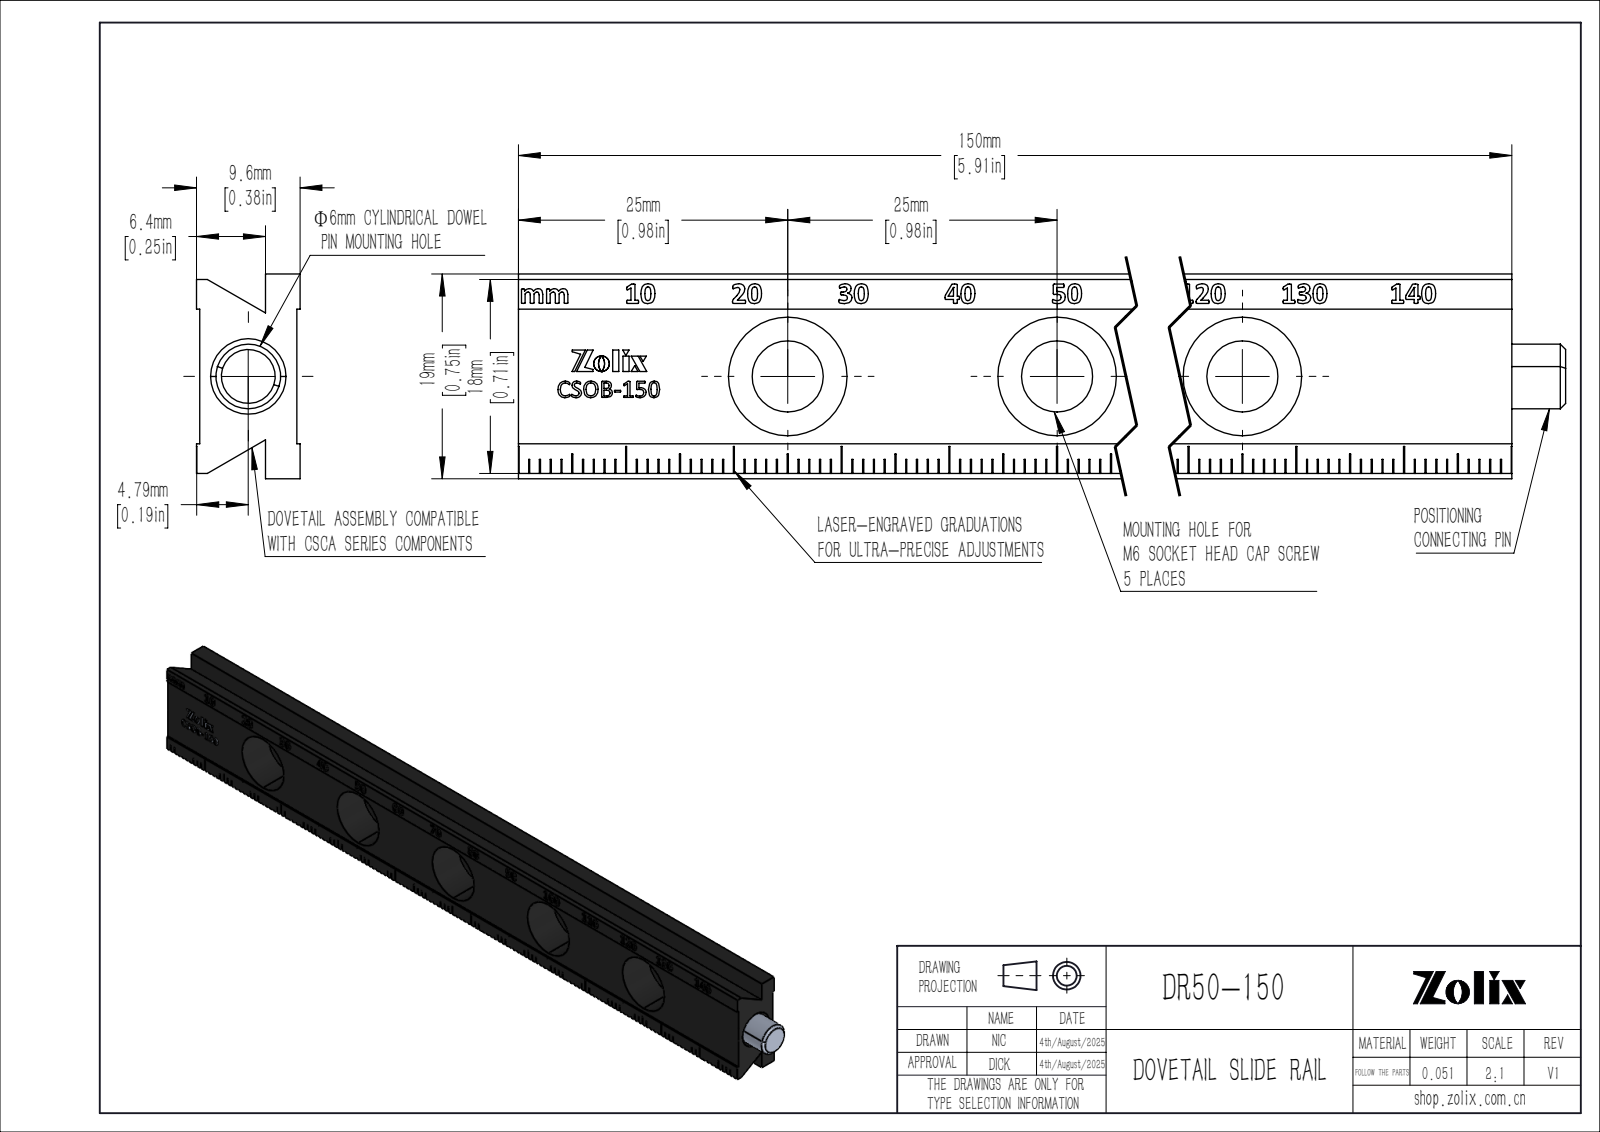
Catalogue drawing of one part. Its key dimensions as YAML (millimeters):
part_name: "CSOB-150"
step_written_by: "SolidWorks 2020 (CONFIG_CONTROL_DESIGN)"
units: millimeters
bodies: {solids: 2, faces: 1003, planar: 892, cylindrical: 26, other: 85}
overall_size: [155, 19, 9.6]
volume: 19070
surface_area: 11756
round_holes:
  - {diameter: 6.6, count: 5}
  - {diameter: 11, count: 5}
  - {diameter: 6, count: 1}
face_to_face_distances: [9.3, 9, 2.9, 6.1, 3.2, 9.6, 6.4, 19, 0.7, 2.5]
hole_center_spacings: [25, 50, 75, 100]
